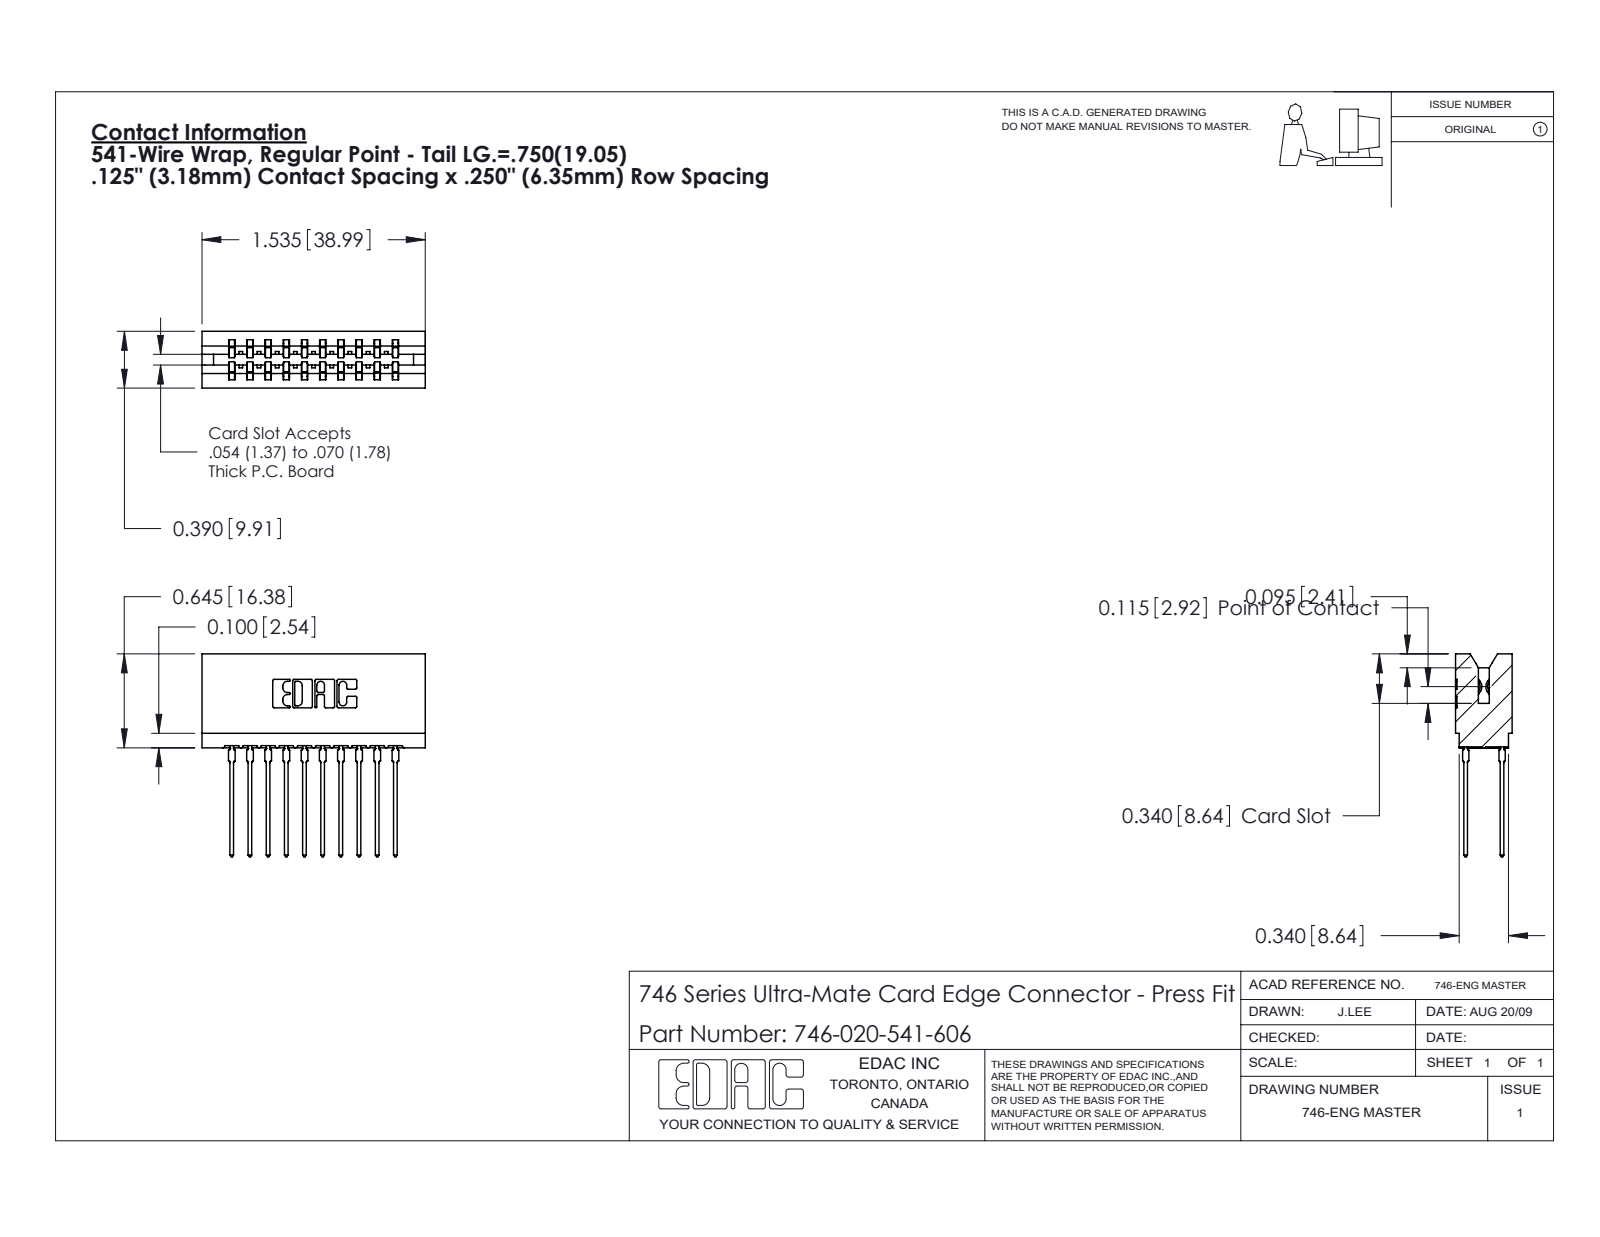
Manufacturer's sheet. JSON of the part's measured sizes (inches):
{"part_name": "746-020-541-606; 746 Part_.340 Slot Depth - 06; 746-292-001_541", "step_written_by": "SolidWorks 2020 (CONFIG_CONTROL_DESIGN)", "units": "inches", "bodies": {"solids": 21, "faces": 1888, "planar": 976, "cylindrical": 392, "other": 520}, "overall_size": [1.535, 1.394, 0.39], "volume_in3": 0.29, "surface_area_in2": 10.73, "partial_cylinders_radius": [[0.021, 40], [0.01, 22], [0.015, 11], [0.005, 8], [0.011, 8], [0.007, 6], [0.031, 6], [0.026, 3]], "face_to_face_distances": [0.25, 0.057, 0.333, 0.5, 0.042, 0.125, 0.083, 0.75, 0.125, 0.025]}
